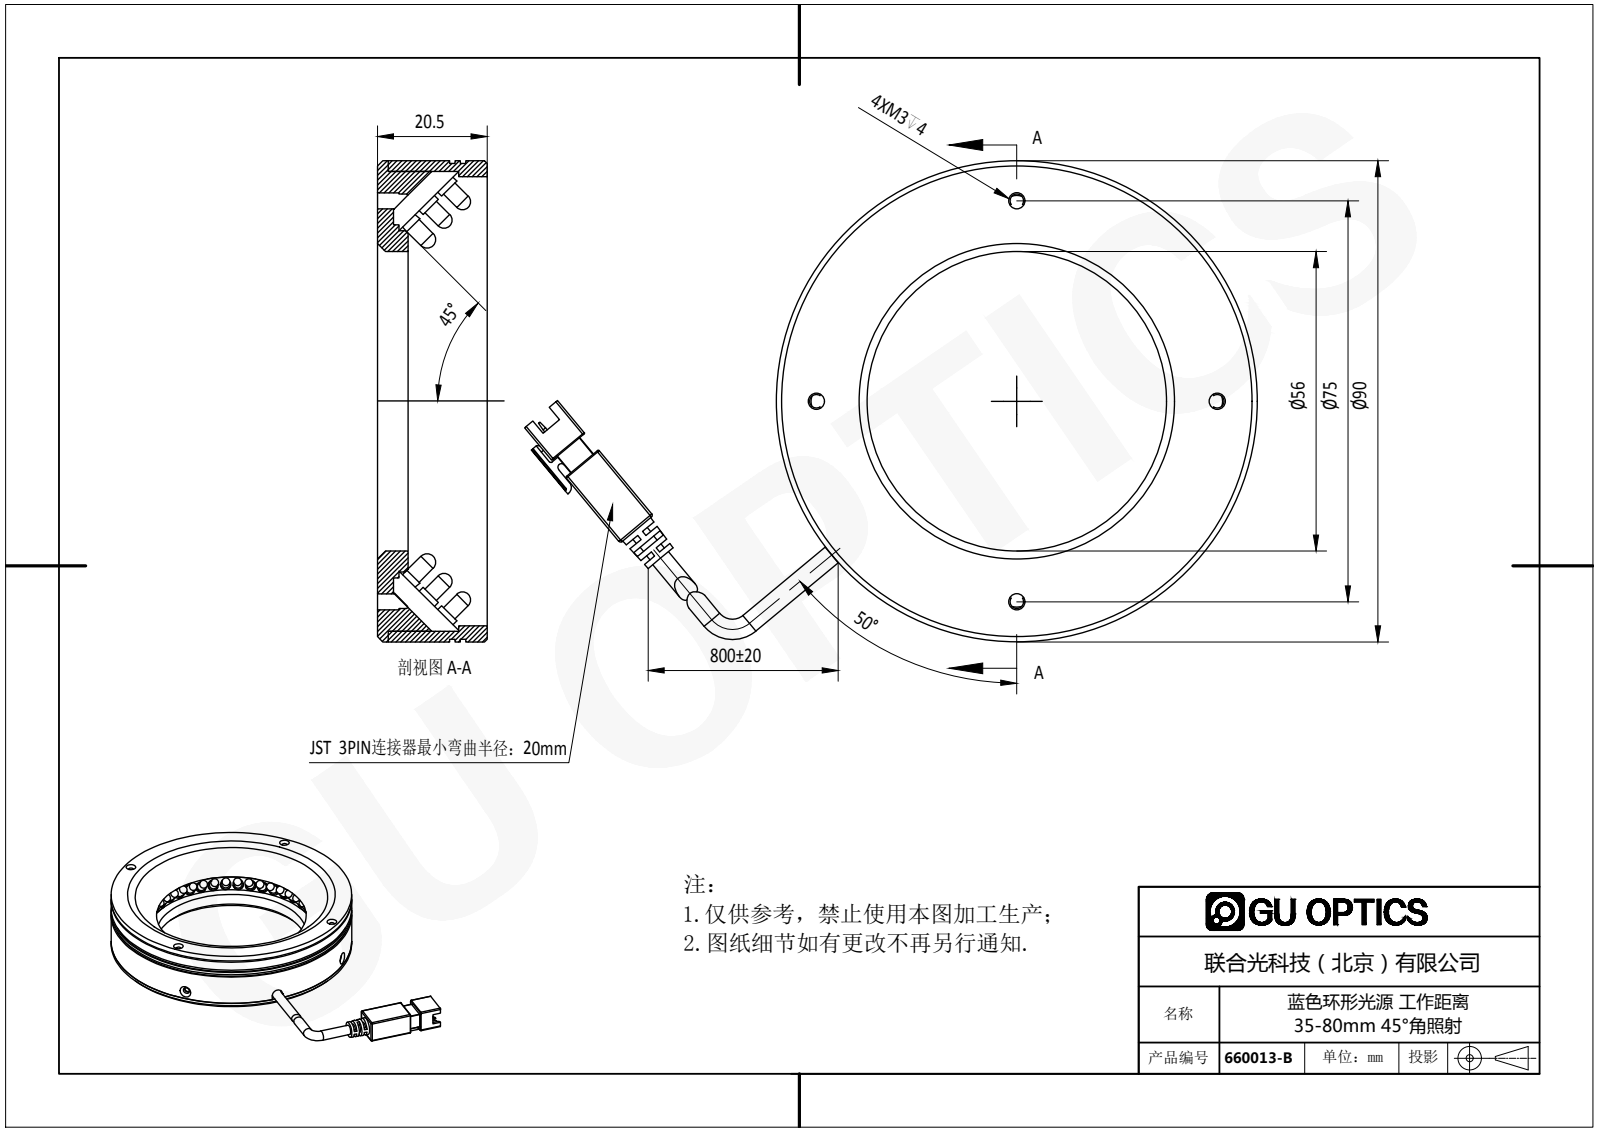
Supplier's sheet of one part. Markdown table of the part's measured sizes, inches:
| quantity | value |
| --- | --- |
| part name | 660013-B |
| STEP written by | SolidWorks 2016 (AUTOMOTIVE_DESIGN) |
| units | inches |
| bodies | 156 solids, 2970 faces (1958 planar, 768 cylindrical, 244 other) |
| overall size | 5.565 × 3.756 × 0.965 |
| volume | 2.984 in³ |
| surface area | 88.78 in² |
| round holes (diameter × count) | 0.049 × 4, 0.063 × 4, 0.071 × 4, 0.079 × 4, 0.118 × 4, 0.138 × 3, 0.094 × 2, 2.205 × 1, 3.307 × 1 |
| round bosses / shafts (diameter × count) | 0.15 × 150, 0.118 × 150, 0.138 × 2, 3.543 × 1, 3.504 × 1, 3.386 × 1, 2.598 × 1, 2.512 × 1 |
| partial cylindrical surfaces (radius × count) | 0.004 × 15, 0.008 × 13, 0.016 × 12, 0.049 × 4, 0.012 × 1, 0.027 × 1, 0.055 × 1, 0.063 × 1 |
| main face-to-face distances | 0.079, 0.807, 0.039, 0.886, 0.728, 0.118, 0.583, 0.146, 0.224, 0.661 |
| hole center spacings | 2.231, 0.157, 0.197, 0.261, 1.476, 1.673, 2.088, 2.366 |
